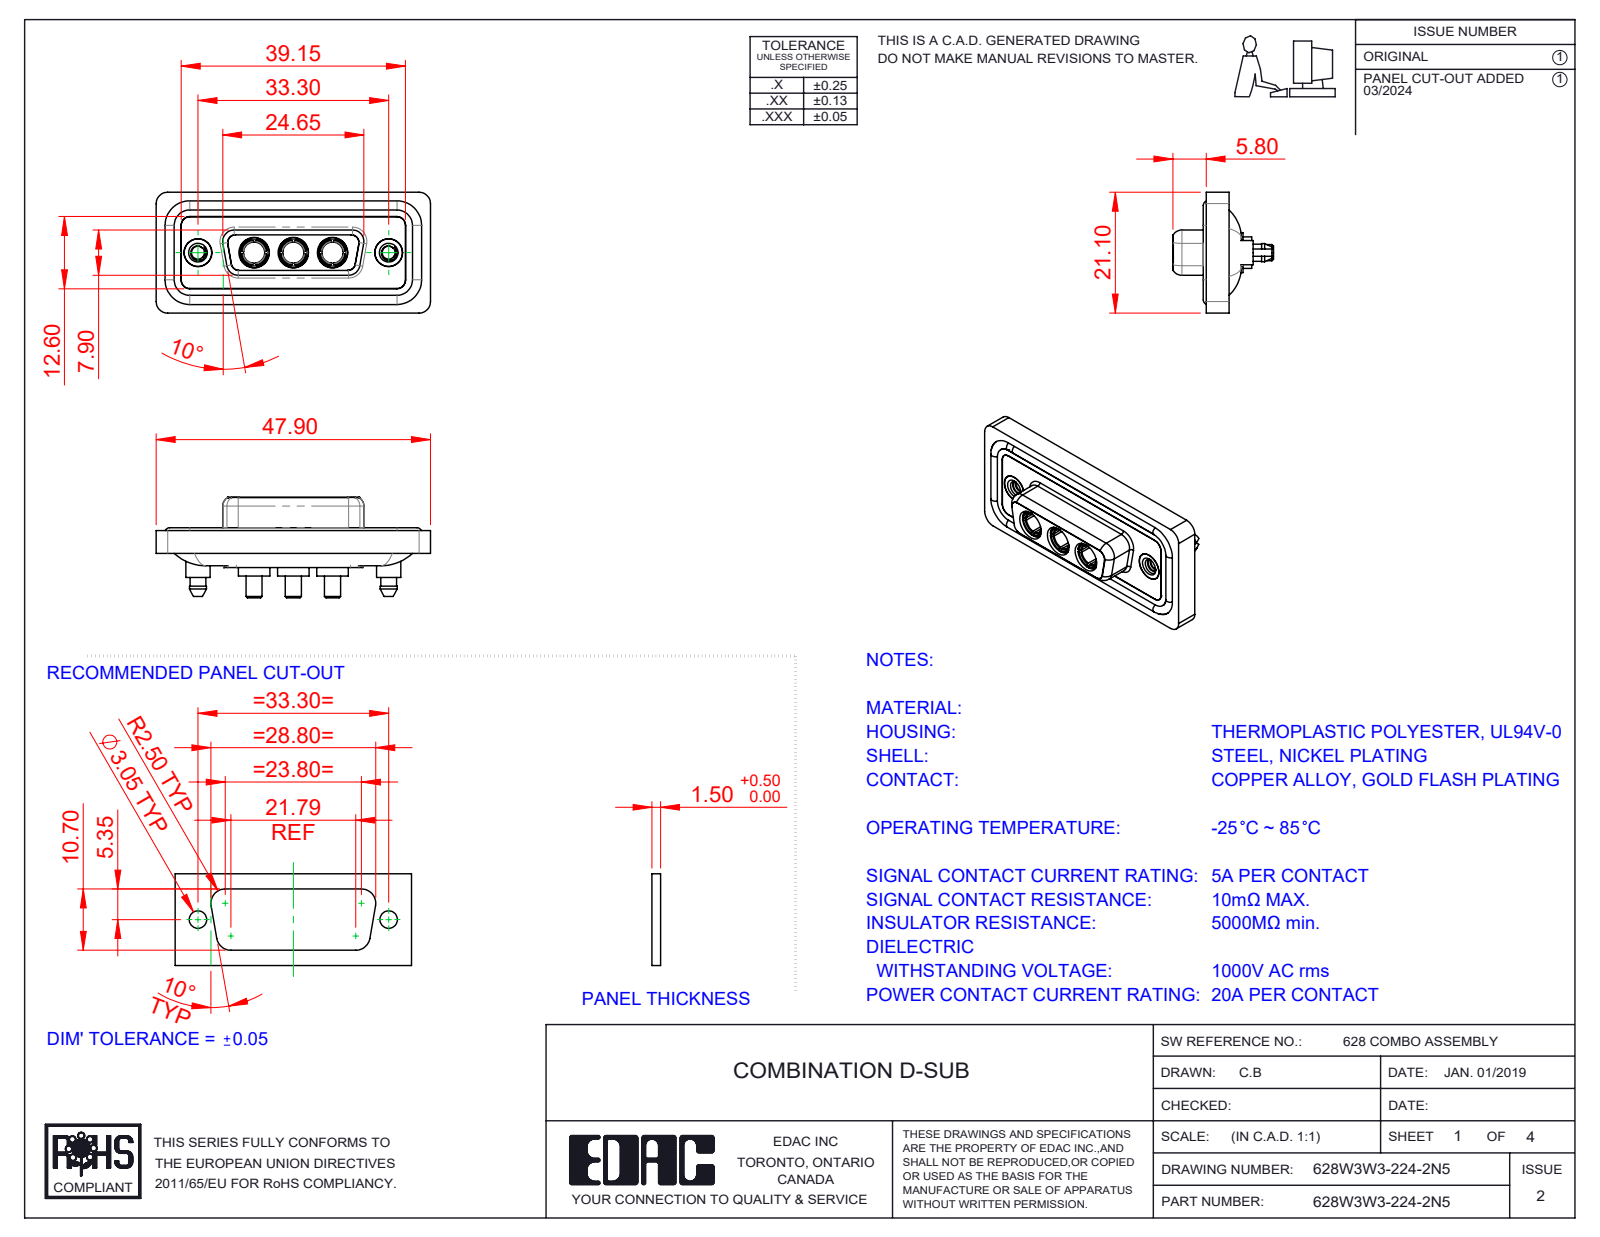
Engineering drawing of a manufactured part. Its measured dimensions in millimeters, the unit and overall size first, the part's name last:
Units: millimetres
Overall size (bounding box): 47.9 × 21.1 × 17.55
Round holes (diameter × count): ⌀4.85 ×5, ⌀3.7 ×3, ⌀5.3 ×3, ⌀2.26 ×2, ⌀4 ×2, ⌀4.05 ×2, ⌀5 ×2
Round bosses / shafts (diameter × count): ⌀1.6 ×4, ⌀5.5 ×3, ⌀5.2 ×3, ⌀4.96 ×3, ⌀4.75 ×3, ⌀3.75 ×3, ⌀2.8 ×3, ⌀5.4 ×2
Partial cylindrical surfaces — rounded edges, fillets, slot ends (radius × count): R1.5 ×24, R2 ×20, R1.35 ×12, R1.6 ×10, R0.25 ×4, R0.5 ×4, R0.6 ×4, R0.65 ×4
Main face-to-face distances: 0.4, 1.8, 1.6, 0.5, 7.45, 1.1, 2.9, 5.65, 7.05, 6.6
Hole centre spacings: 6.85, 9.8, 16.65, 23.5, 13.7, 33.3
Volume: 6 160 mm³ · Surface area: 10 072 mm²
Bodies: 13 solids, 658 faces (208 planar, 289 cylindrical, 161 other)
Part name (STEP PRODUCT): 628Combo Housing_3W3; 628Combo Waterproof Housing_15 Contacts; 628Combo Shell Rear_15 Contacts; 628Combo Threaded Boardlock_5 (+3 more)
STEP written by: SolidWorks 2023 (CONFIG_CONTROL_DESIGN)
